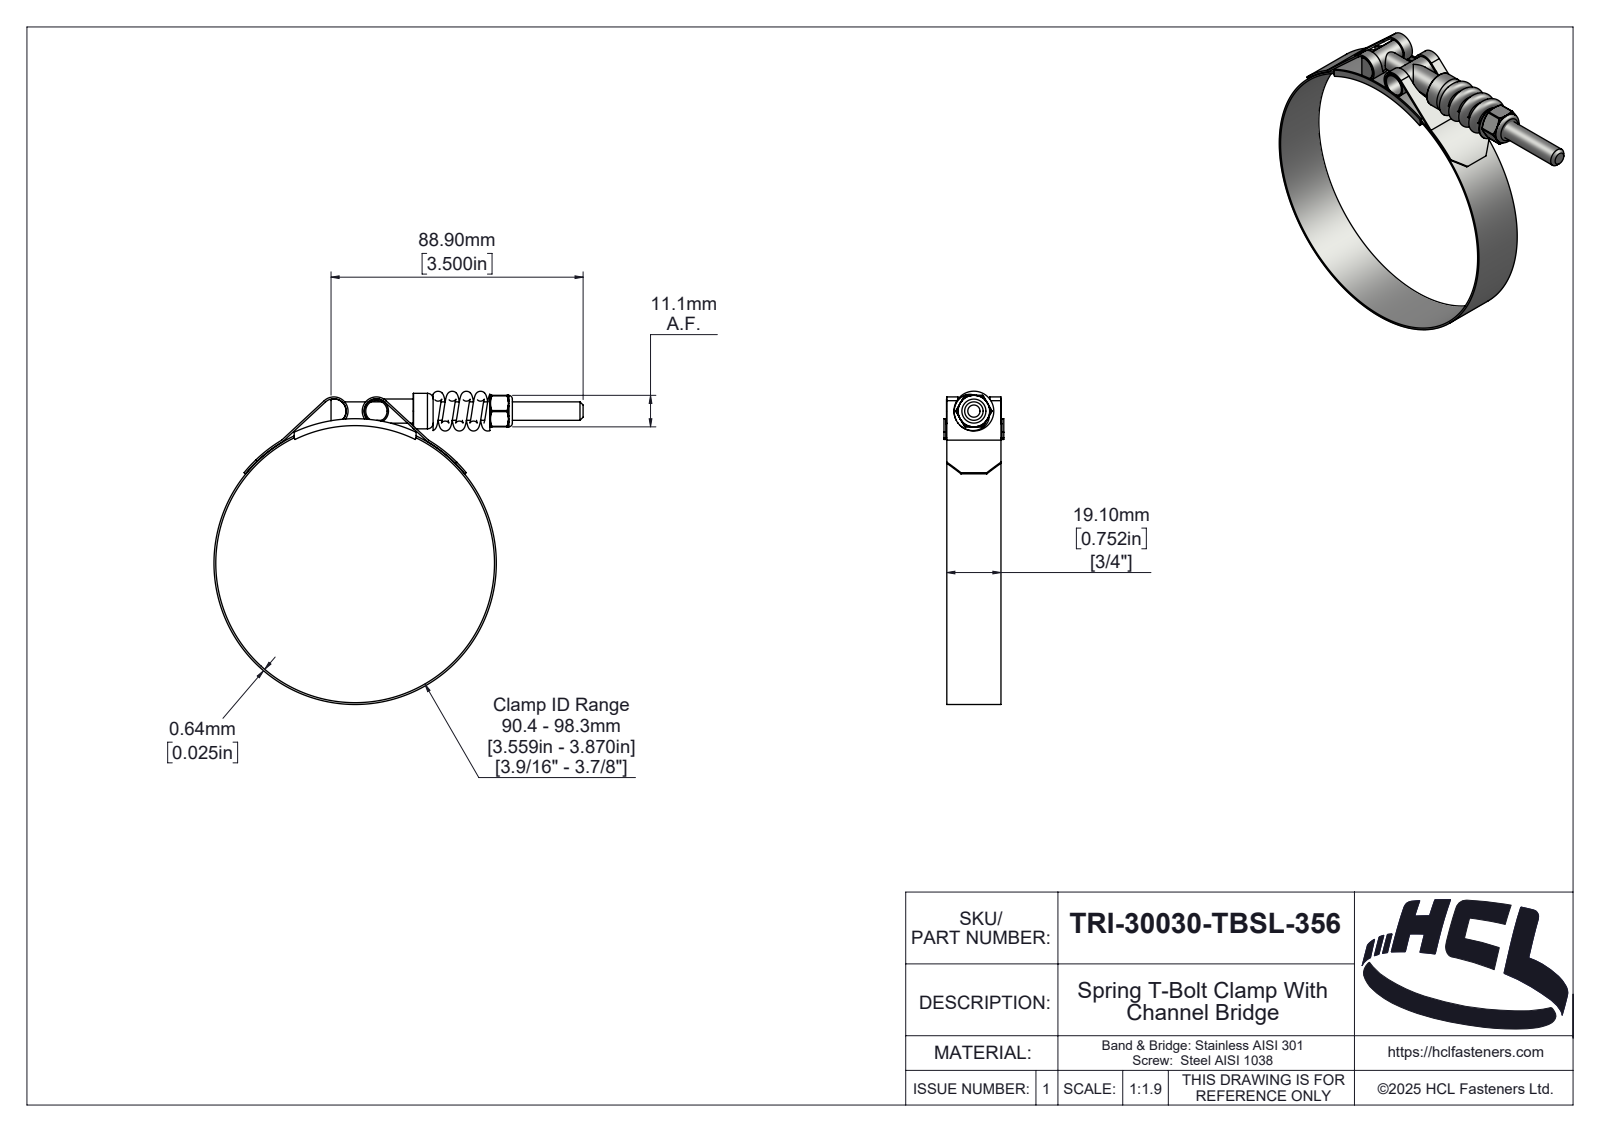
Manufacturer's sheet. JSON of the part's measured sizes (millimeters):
{"part_name": "TRI-30030-TBSL-356", "step_written_by": "SolidWorks 2025 (AUTOMOTIVE_DESIGN)", "units": "millimeters", "bodies": {"solids": 7, "faces": 332, "planar": 48, "cylindrical": 122, "other": 162}, "overall_size": [131.19, 110.44, 21.1], "volume_mm3": 11756, "surface_area_mm2": 23908, "round_holes": [[5.4, 1], [6.35, 1], [6.5, 1], [7.52, 1], [98.3, 1]], "round_bosses_or_shafts": [[8.52, 2], [99.58, 1], [12.52, 1]], "partial_cylinders_radius": [[0.39, 6], [0.5, 2], [4.36, 2], [5, 2], [0.59, 1], [2.42, 1], [3.03, 1], [3.19, 1]], "face_to_face_distances": [0.64, 19.1, 1, 20.1, 20.46, 0.36, 19.46, 56, 21.1, 11.11], "hole_center_spacings": [54.15]}
